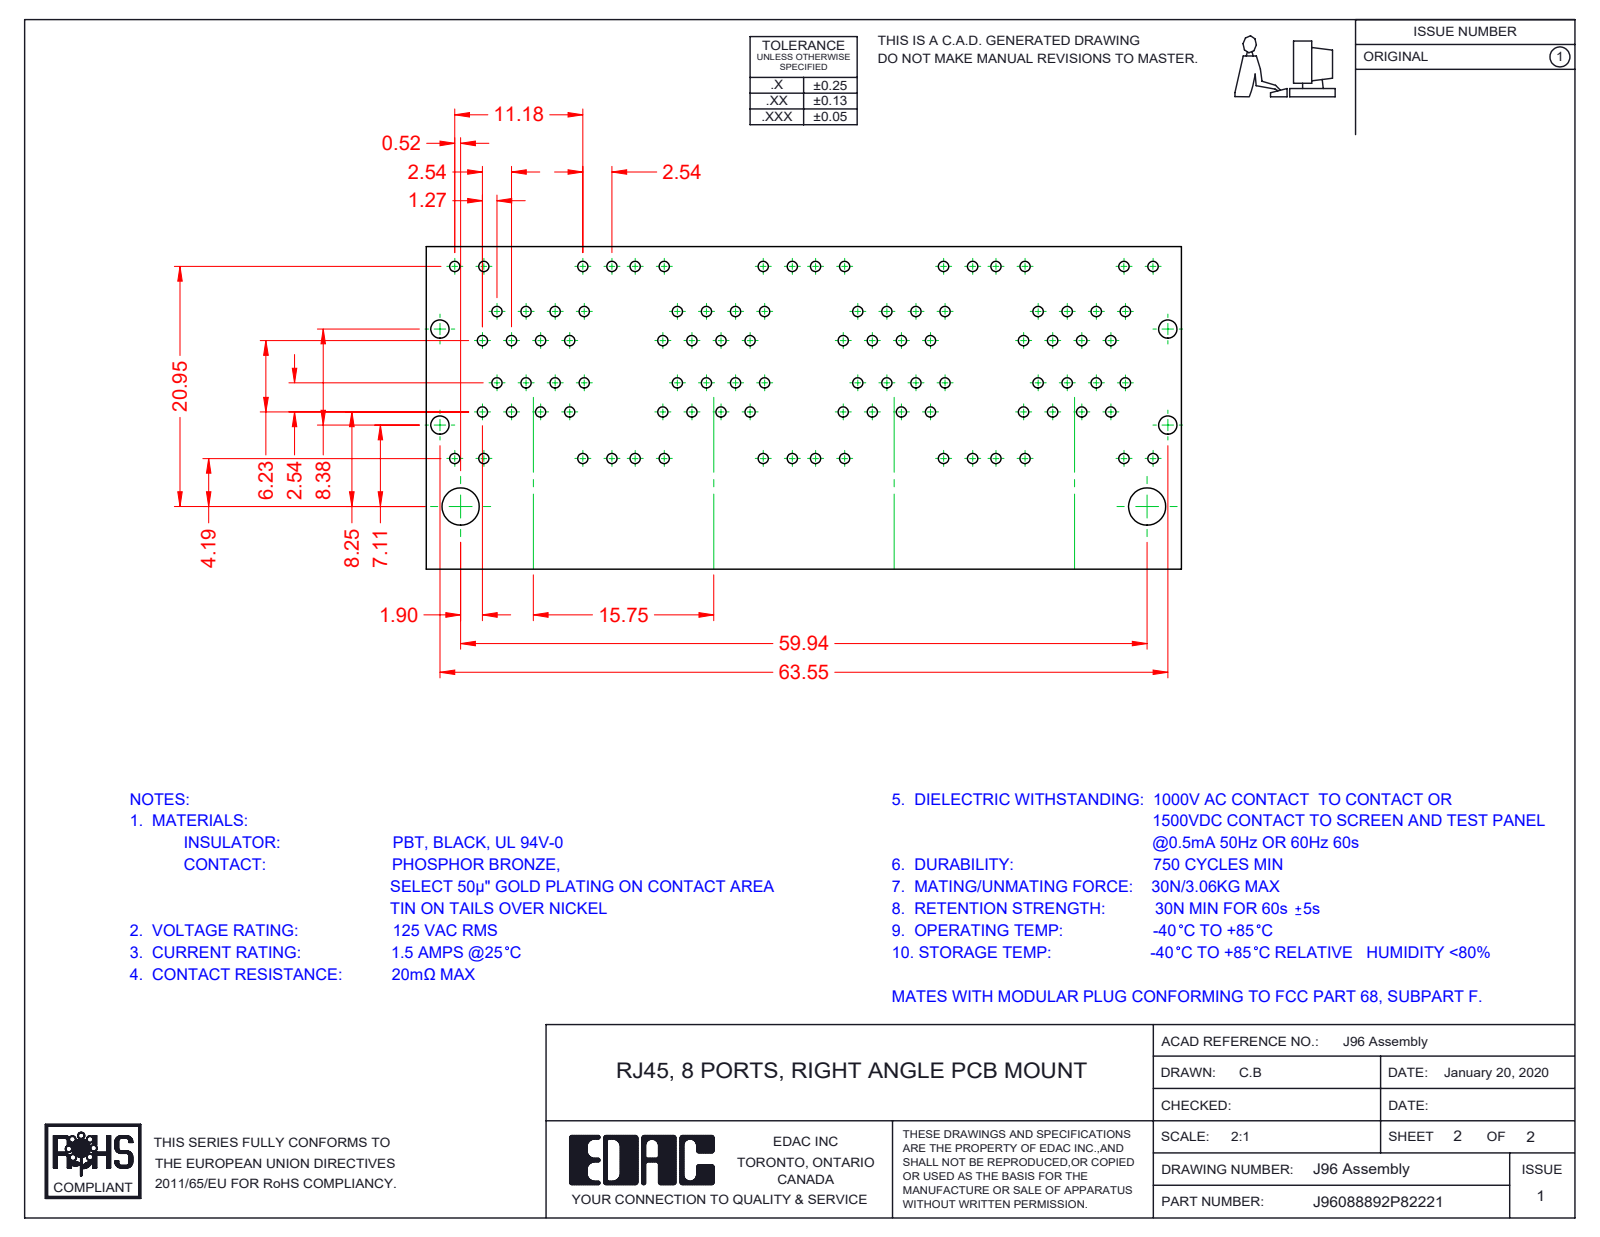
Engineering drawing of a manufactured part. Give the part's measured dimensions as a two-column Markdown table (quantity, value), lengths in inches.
| quantity | value |
| --- | --- |
| part name | 96 LED RH Lower_2-Red; 96 Back Plate_8 Ports; 96 Contacts Upper; 96 Contact Lock Upper (+8 more) |
| STEP written by | SolidWorks 2016 (CONFIG_CONTROL_DESIGN) |
| units | inches |
| bodies | 96 solids, 7820 faces (6105 planar, 1404 cylindrical, 311 other) |
| overall size | 2.652 × 1.235 × 1.129 |
| volume | 1.474 in³ |
| surface area | 98.57 in² |
| round holes (diameter × count) | 0.067 × 3 |
| round bosses / shafts (diameter × count) | 0.066 × 3 |
| partial cylindrical surfaces (radius × count) | 0.01 × 124, 0.014 × 73, 0.039 × 72, 0.02 × 49, 0.036 × 32, 0.008 × 27, 0.011 × 14, 0.028 × 11 |
| main face-to-face distances | 0.62, 0.014, 0.392, 0.046, 0.063, 0.021, 0.393, 0.401, 0.499, 0.133 |
| hole center spacings | 0.62, 1.24 |
